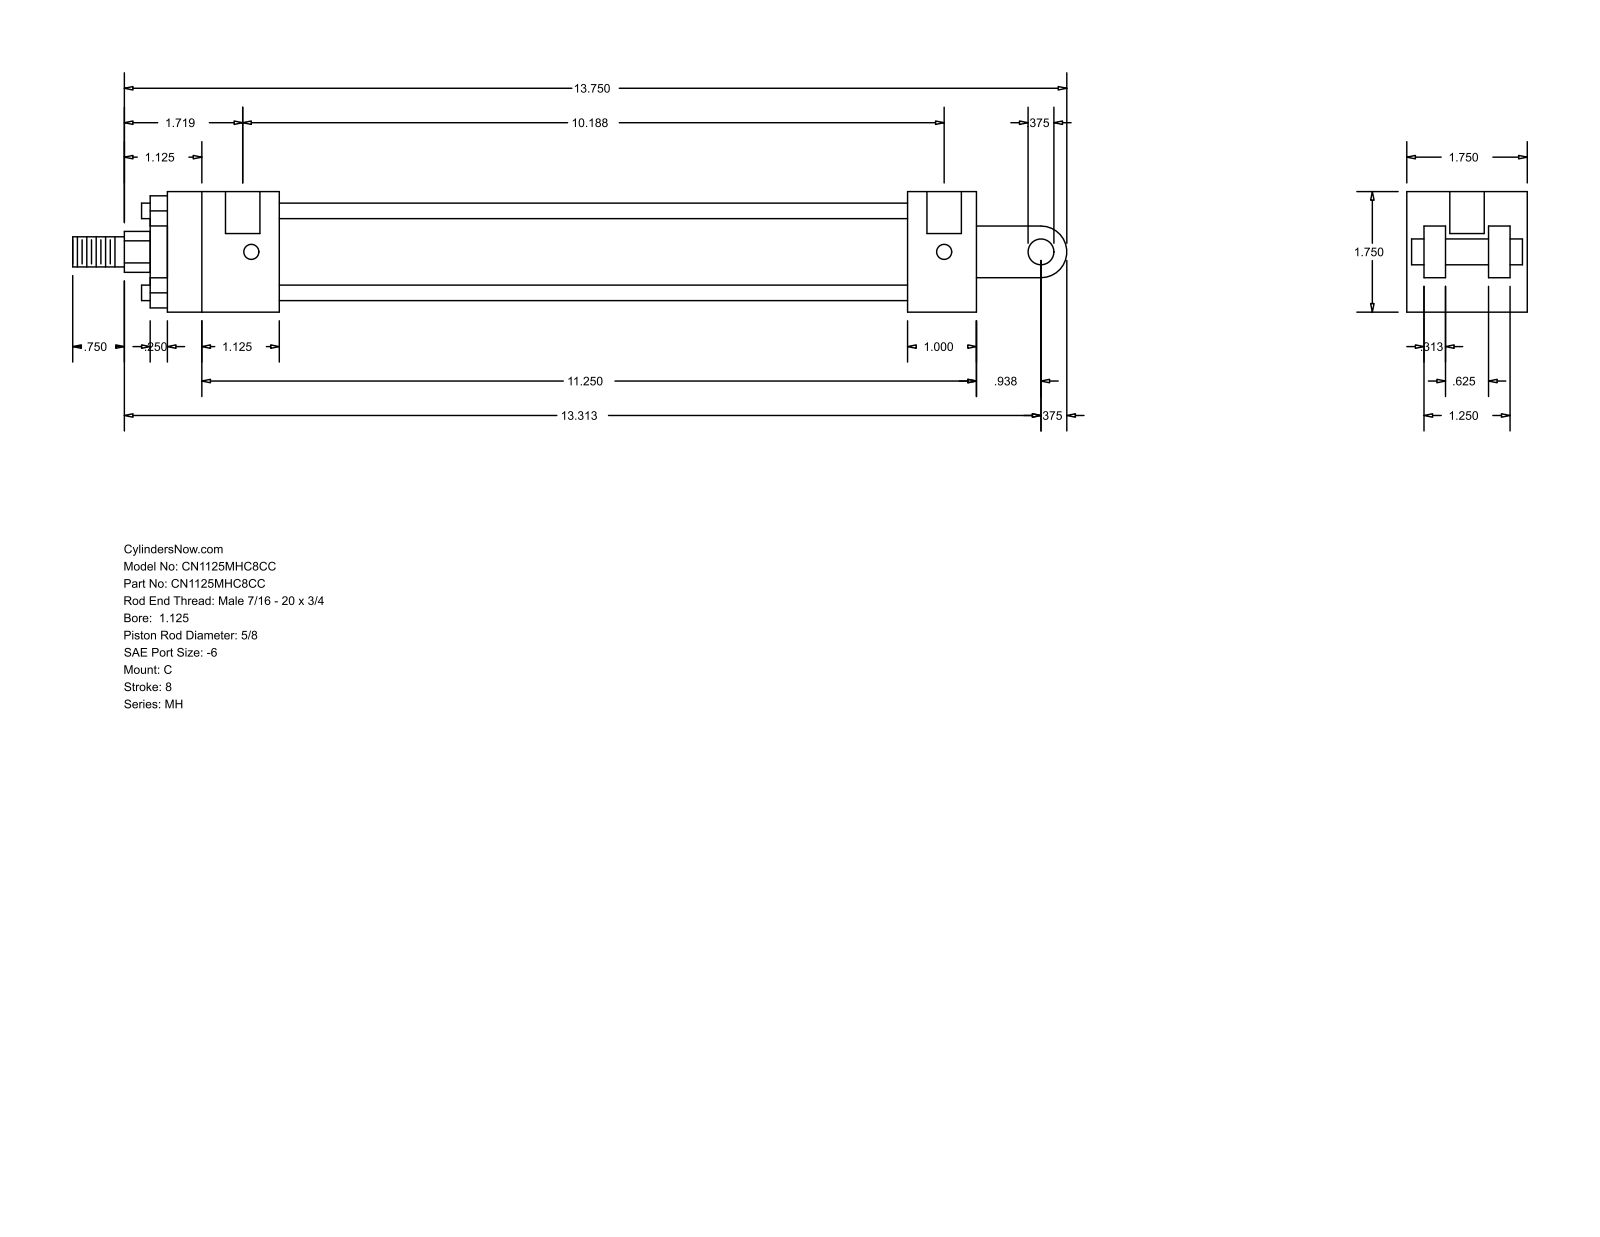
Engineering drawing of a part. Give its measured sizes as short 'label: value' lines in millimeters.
name: MH_C__0112_0.625
written by: GSSL Pune (CONFIG_CONTROL_DESIGN)
unit: mm
bodies: 0 solids, 99 faces (70 planar, 29 cylindrical, 0 other)
size: 366.71 × 44.45 × 44.45
holes: 4× ⌀5.56, 2× ⌀12.7
bosses: 4× ⌀5.71, 1× ⌀34.92, 1× ⌀28.57, 1× ⌀15.88, 1× ⌀11.11, 1× ⌀9.53
rounds: 1× R7.54, 1× R9.53
face distances: 44.46, 6.35, 31.76, 14.29, 30.17, 38.11, 7.94, 23.82, 12.7, 41.27
hole spacings: 255.59, 3.17, 258.76
